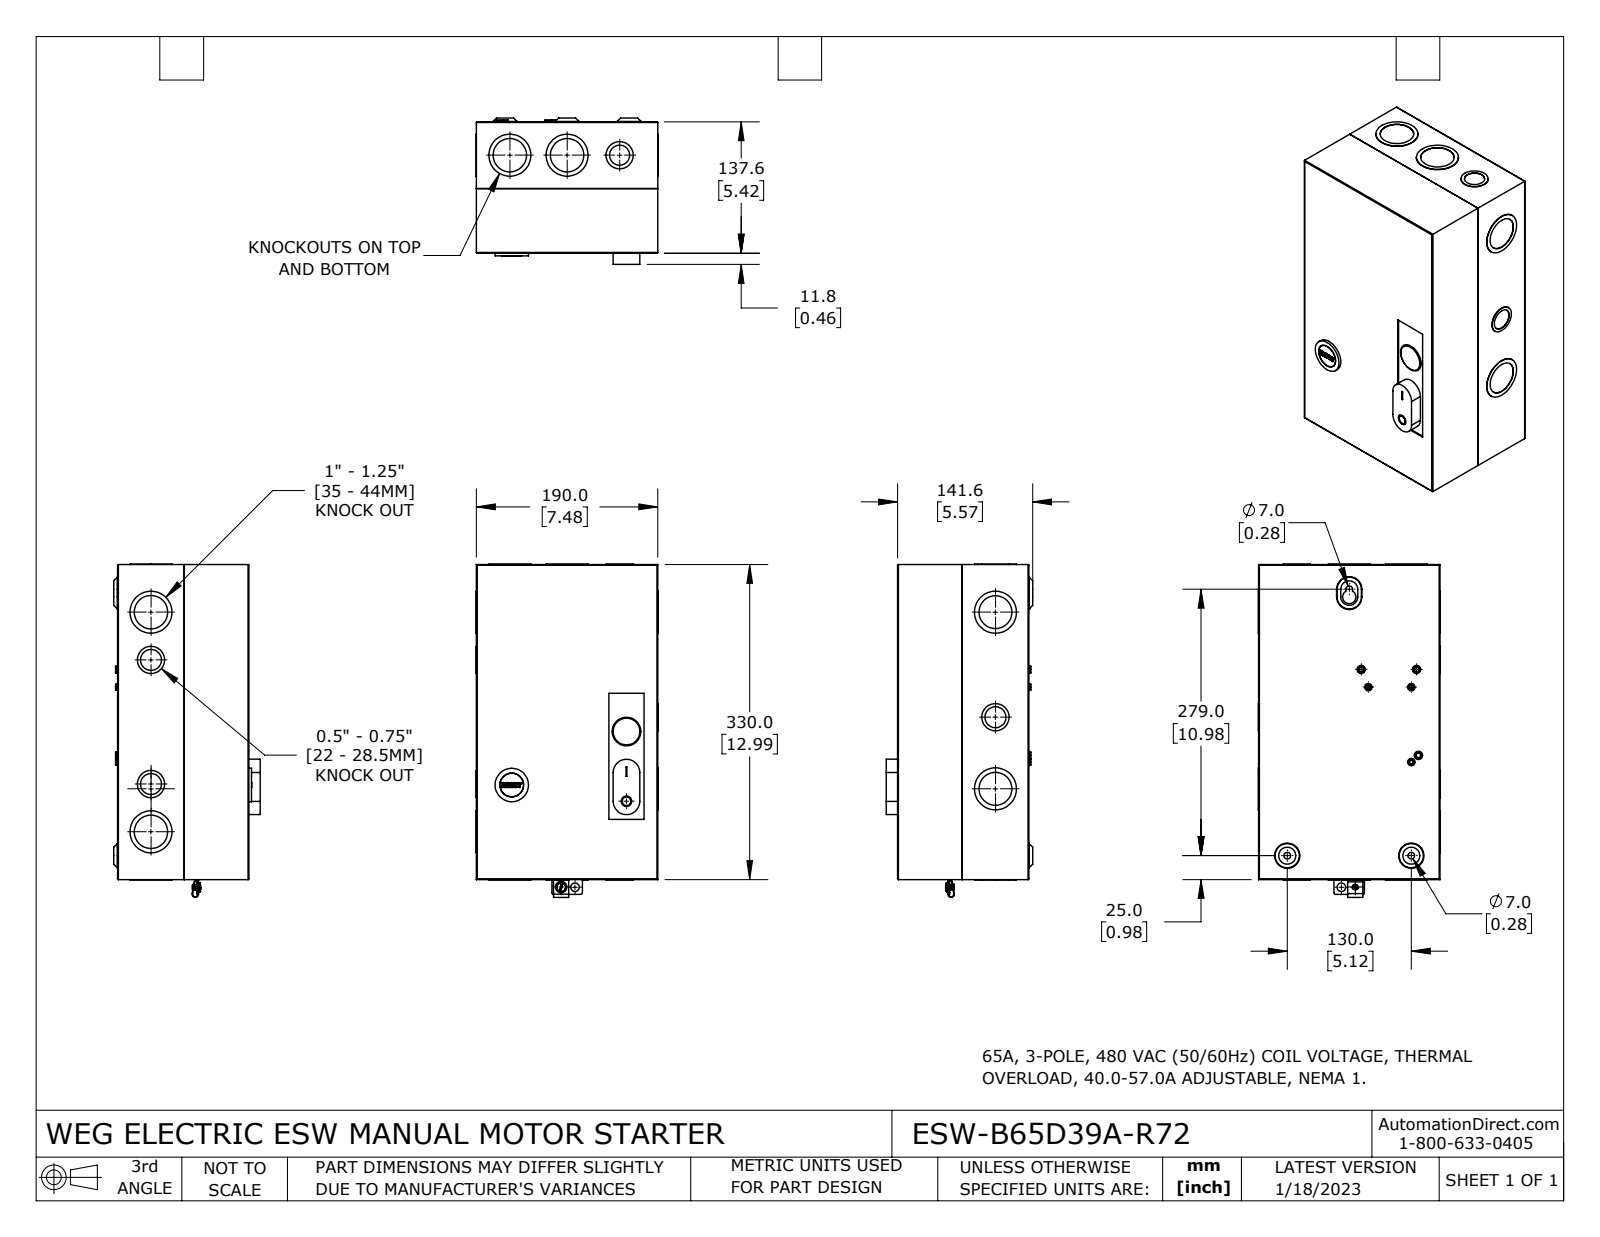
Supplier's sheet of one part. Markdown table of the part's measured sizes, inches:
| quantity | value |
| --- | --- |
| part name | ESW-B65D39A-R72 |
| STEP written by | SolidWorks 2021 (CONFIG_CONTROL_DESIGN) |
| units | inches |
| bodies | 7 solids, 435 faces (161 planar, 221 cylindrical, 53 other) |
| overall size | 13.74 × 7.504 × 6.039 |
| volume | 24.58 in³ |
| surface area | 936.7 in² |
| round holes (diameter × count) | 1.378 × 4, 0.146 × 3, 0.183 × 3, 0.276 × 2, 0.866 × 2, 0.886 × 2, 1.357 × 2, 0.256 × 1, 0.279 × 1, 0.354 × 1, 0.433 × 1, 0.469 × 1 |
| round bosses / shafts (diameter × count) | 1.732 × 4, 1.122 × 3, 0.278 × 3, 0.24 × 3, 1.734 × 2, 1.378 × 1, 1.193 × 1, 1.148 × 1 |
| partial cylindrical surfaces (radius × count) | 0.004 × 34, 0.031 × 8, 0.079 × 3, 0.138 × 3, 0.059 × 2, 0.075 × 2, 0.108 × 2, 0.122 × 2 |
| main face-to-face distances | 0.047, 5.37, 7.433, 5.323, 5.417, 12.945, 7.386, 7.48, 0.071, 12.898 |
| hole center spacings | 0.571, 1.772, 1.969, 2.283, 2.362, 5.118, 7.087, 10.972 |
